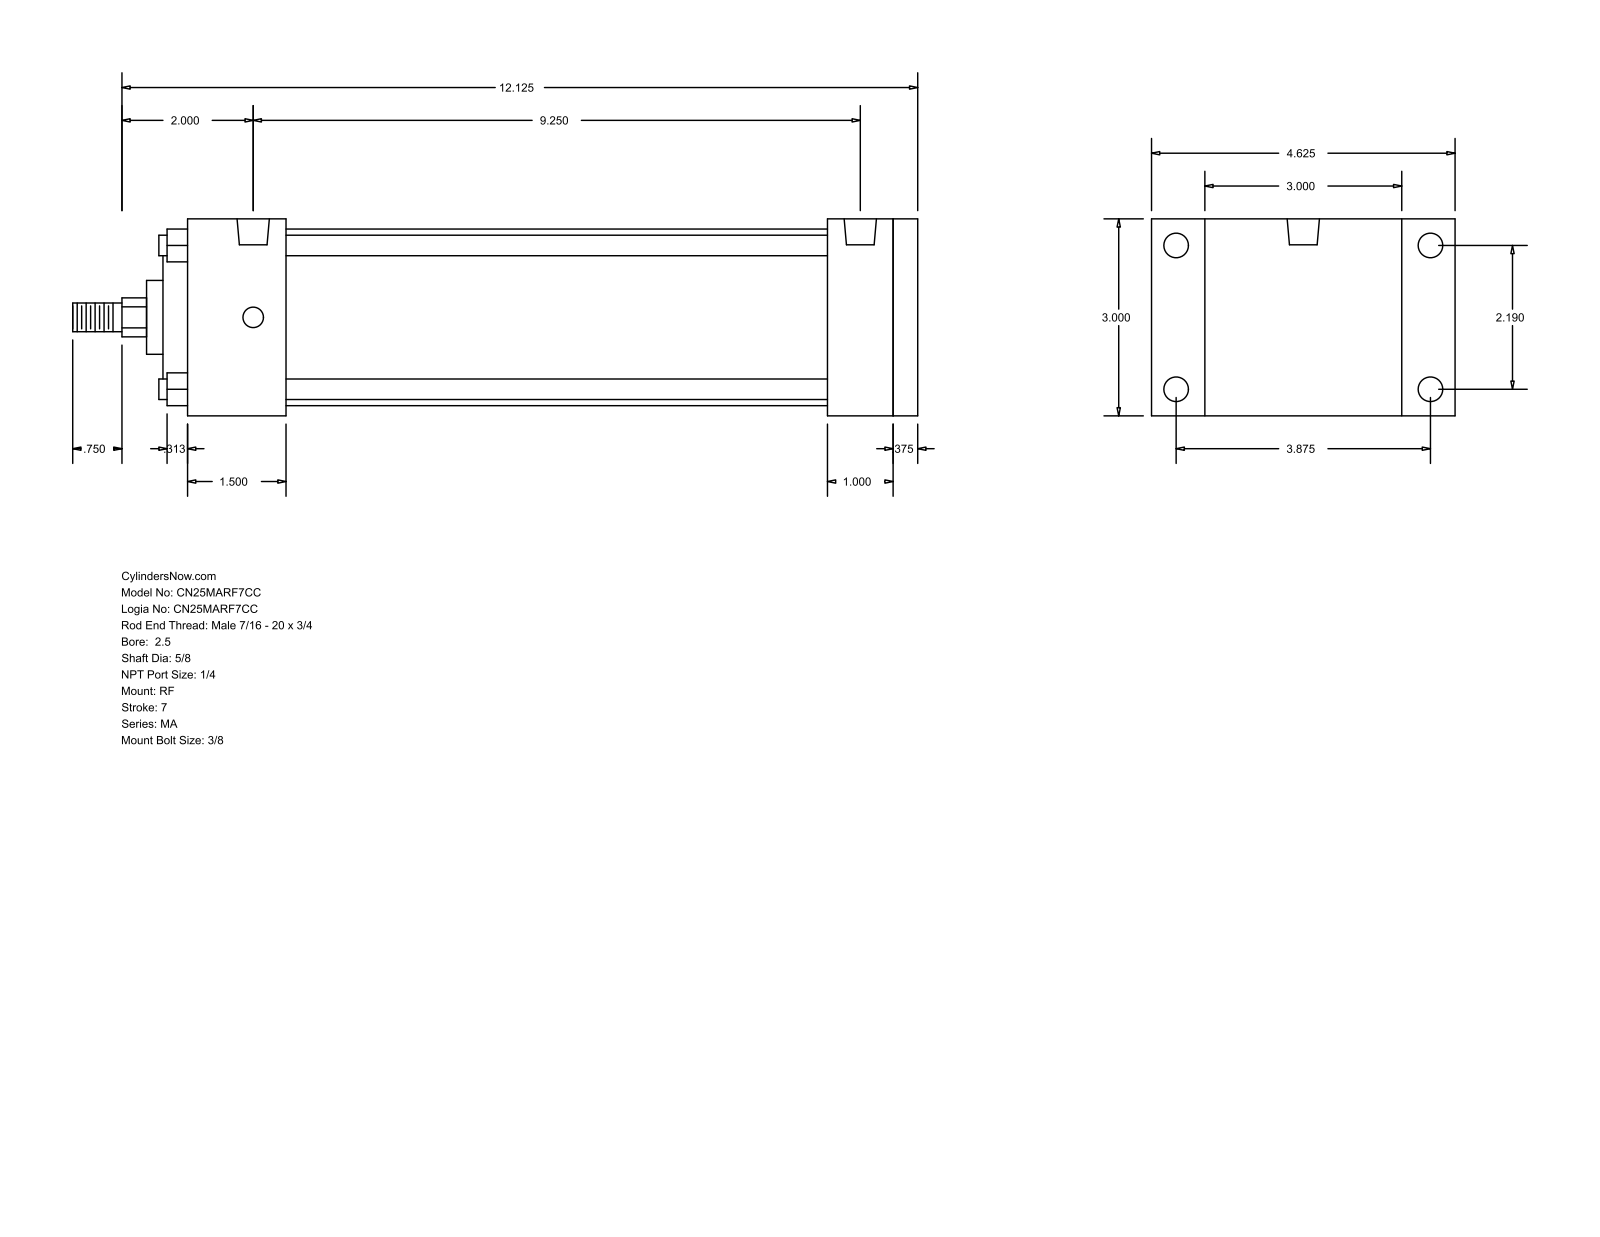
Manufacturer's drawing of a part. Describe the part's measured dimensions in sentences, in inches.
The part is named "MA_RF__0250_0.625". Its 3-D file was written by "GSSL Pune (CONFIG_CONTROL_DESIGN)". It is 0 solids with 94 faces: 65 planar, 29 cylindrical and 0 other. Overall it measures 12.875 by 4.625 by 3 inches. Round holes: 4 of diameter 0.313, 4 of diameter 0.375, 2 of diameter 0.492. Round bosses or shafts: 4 of diameter 0.313, 1 of diameter 2.69, 1 of diameter 2, 1 of diameter 1.125, 1 of diameter 0.625, 1 of diameter 0.437. Partial cylindrical surfaces (rounded edges, fillets, slot ends): 1 of radius 0.297. The main face-to-face distances are 3, 11.125, 0.375, 10.75, 1, 1.375, 1.5, 9.75, 8.25, 9.25. The hole center spacings are 2.19, 3.875, 4.451, 9.25.
